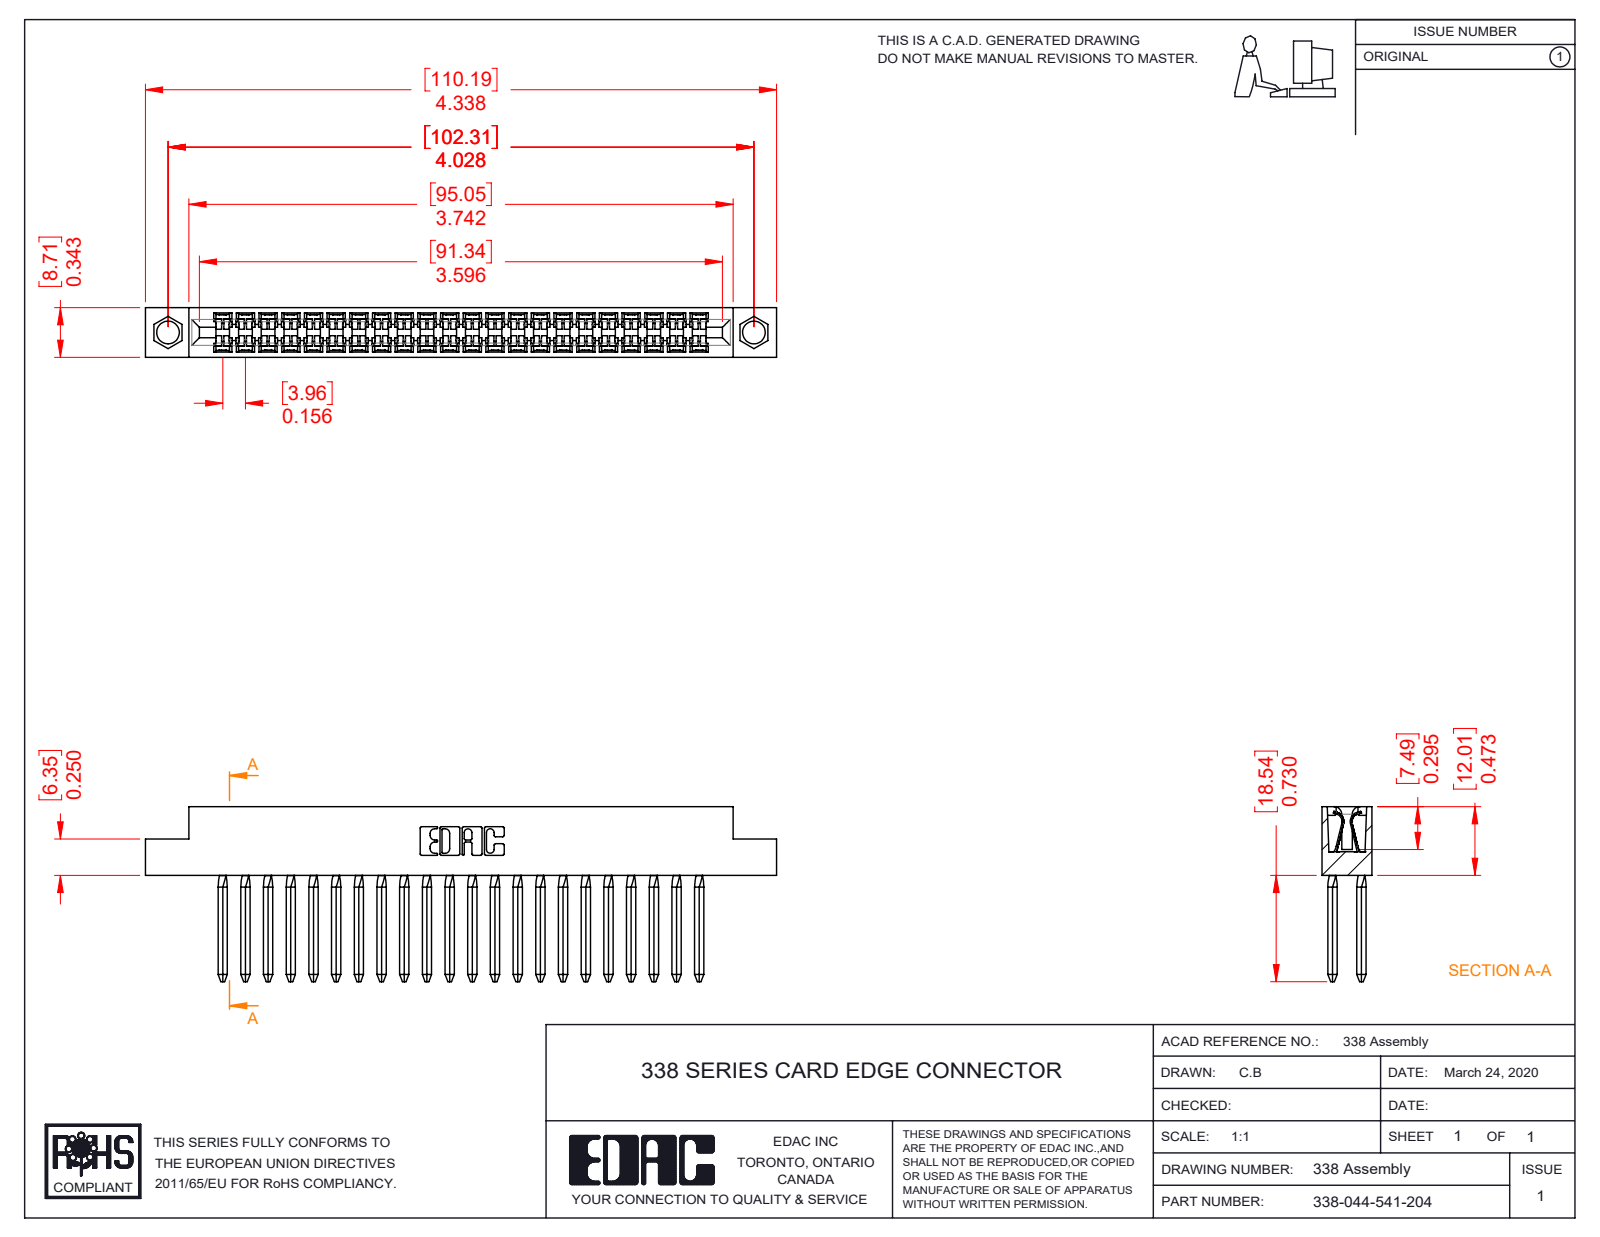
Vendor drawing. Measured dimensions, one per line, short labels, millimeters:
name: 338-044-541-204; 338-290-001_541; 338-210-001_338-210-022-004
written by: SolidWorks 2016 (CONFIG_CONTROL_DESIGN)
unit: mm
bodies: 45 solids, 3056 faces (2132 planar, 748 cylindrical, 176 other)
size: 110.2 × 30.6 × 8.7
volume: 8 360 mm³; area: 15 350 mm²
holes: 2× ⌀4
rounds: 134× R0.6, 44× R0.2, 36× R1.4, 36× R1.7, 35× R2.5, 22× R0.3, 6× R0.2, 6× R0.8
face distances: 8.7, 4, 2.8, 15.8, 5.3, 3.4, 19.8, 11.9, 5.6, 11.2
hole spacings: 102.3
